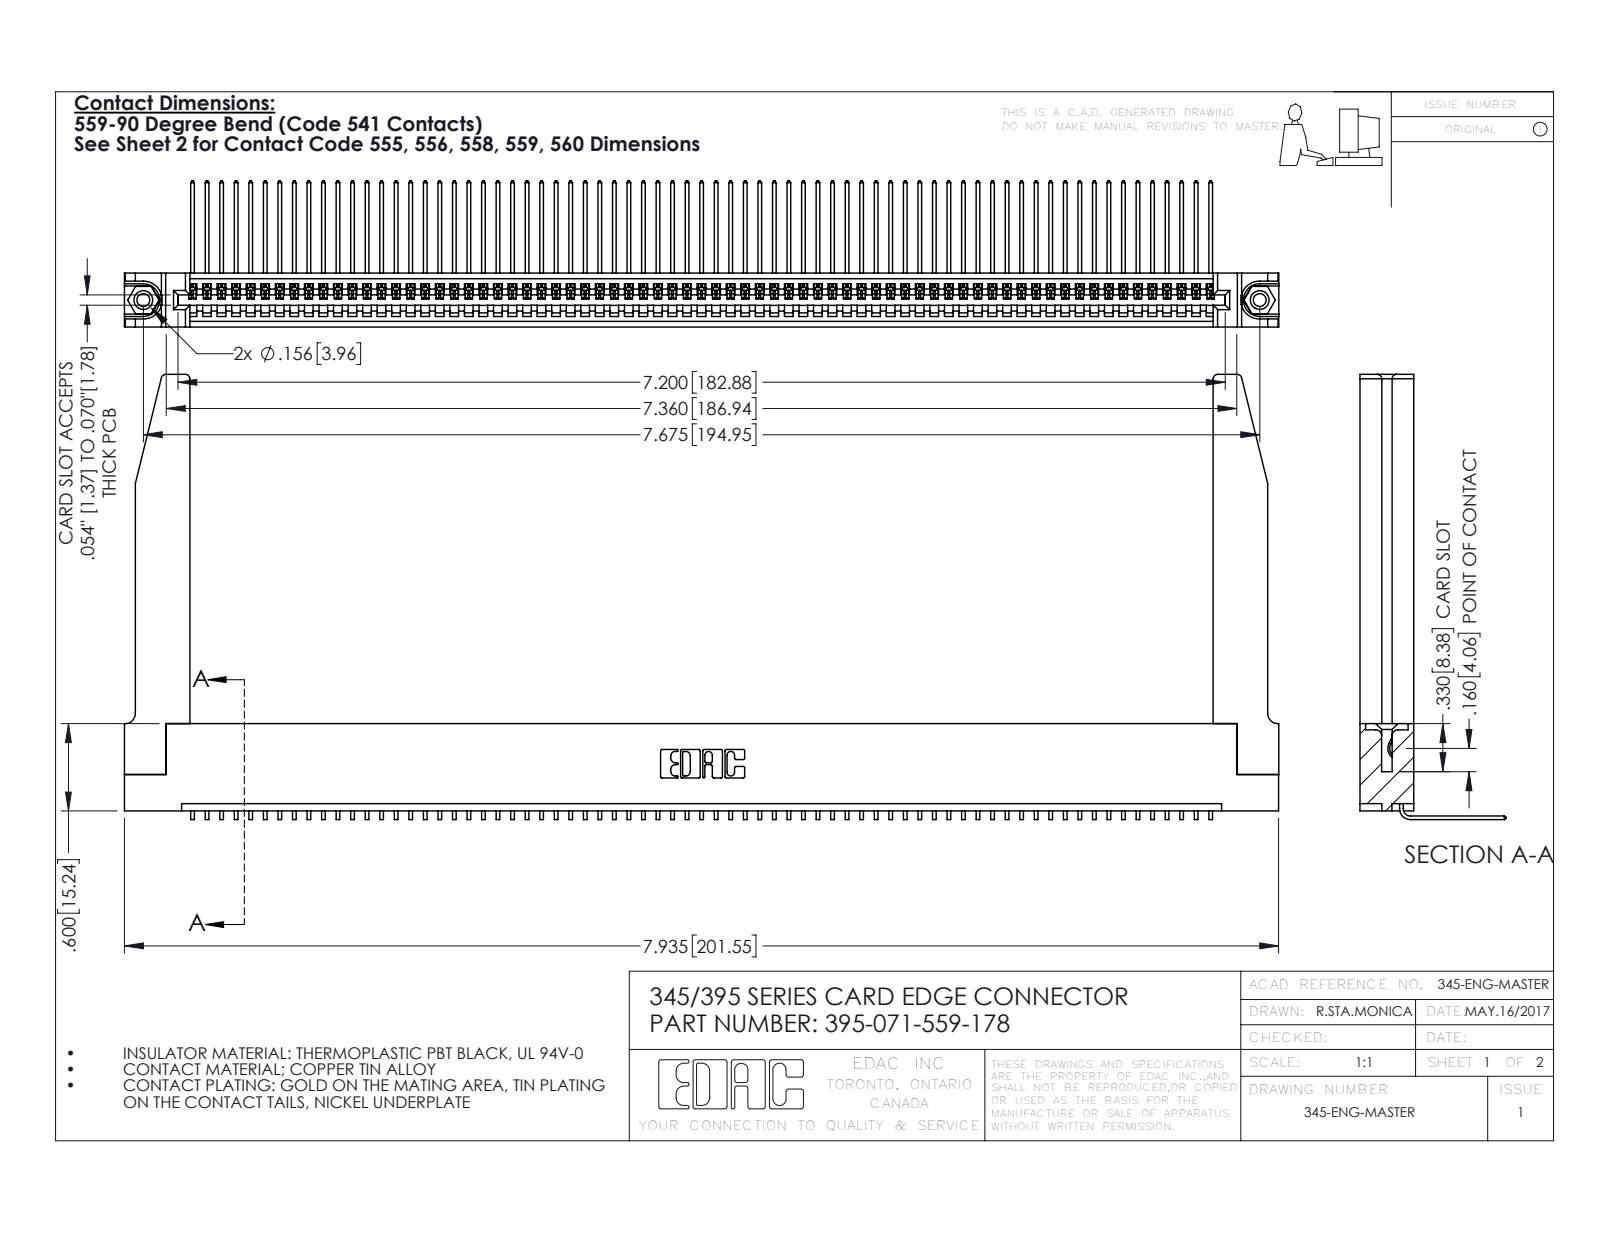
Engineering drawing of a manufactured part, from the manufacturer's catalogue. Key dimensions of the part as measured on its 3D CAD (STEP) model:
Part name (STEP PRODUCT): 345-292-001_558 559 Tail - 1; 395-071-559-178; 345-250-001_345-250-001-102; 345 Part_Flush Mounting Lugs - 0.156 Dia-TH (+1 more)
STEP written by: SolidWorks 2016 (CONFIG_CONTROL_DESIGN)
Units: inches
Bodies: 76 solids, 4620 faces (3204 planar, 1364 cylindrical, 52 other)
Overall size (bounding box): 7.936 × 3.059 × 1.005
Volume: 1.671 in³ · Surface area: 53.79 in²
Round holes (diameter × count): ⌀0.089 ×2, ⌀0.125 ×2, ⌀0.156 ×2, ⌀0.064 ×1
Round bosses / shafts (diameter × count): ⌀0.155 ×2
Partial cylindrical surfaces — rounded edges, fillets, slot ends (radius × count): R0.006 ×142, R0.01 ×22, R0.03 ×8, R0.007 ×6, R0.031 ×6, R0.026 ×3, R0.031 ×2, R0.04 ×2
Main face-to-face distances: 0.072, 0.37, 0.298, 0.2, 0.098, 0.272, 0.025, 0.225, 0.149, 0.148
Hole centre spacings: 0.27, 7.439, 7.675
